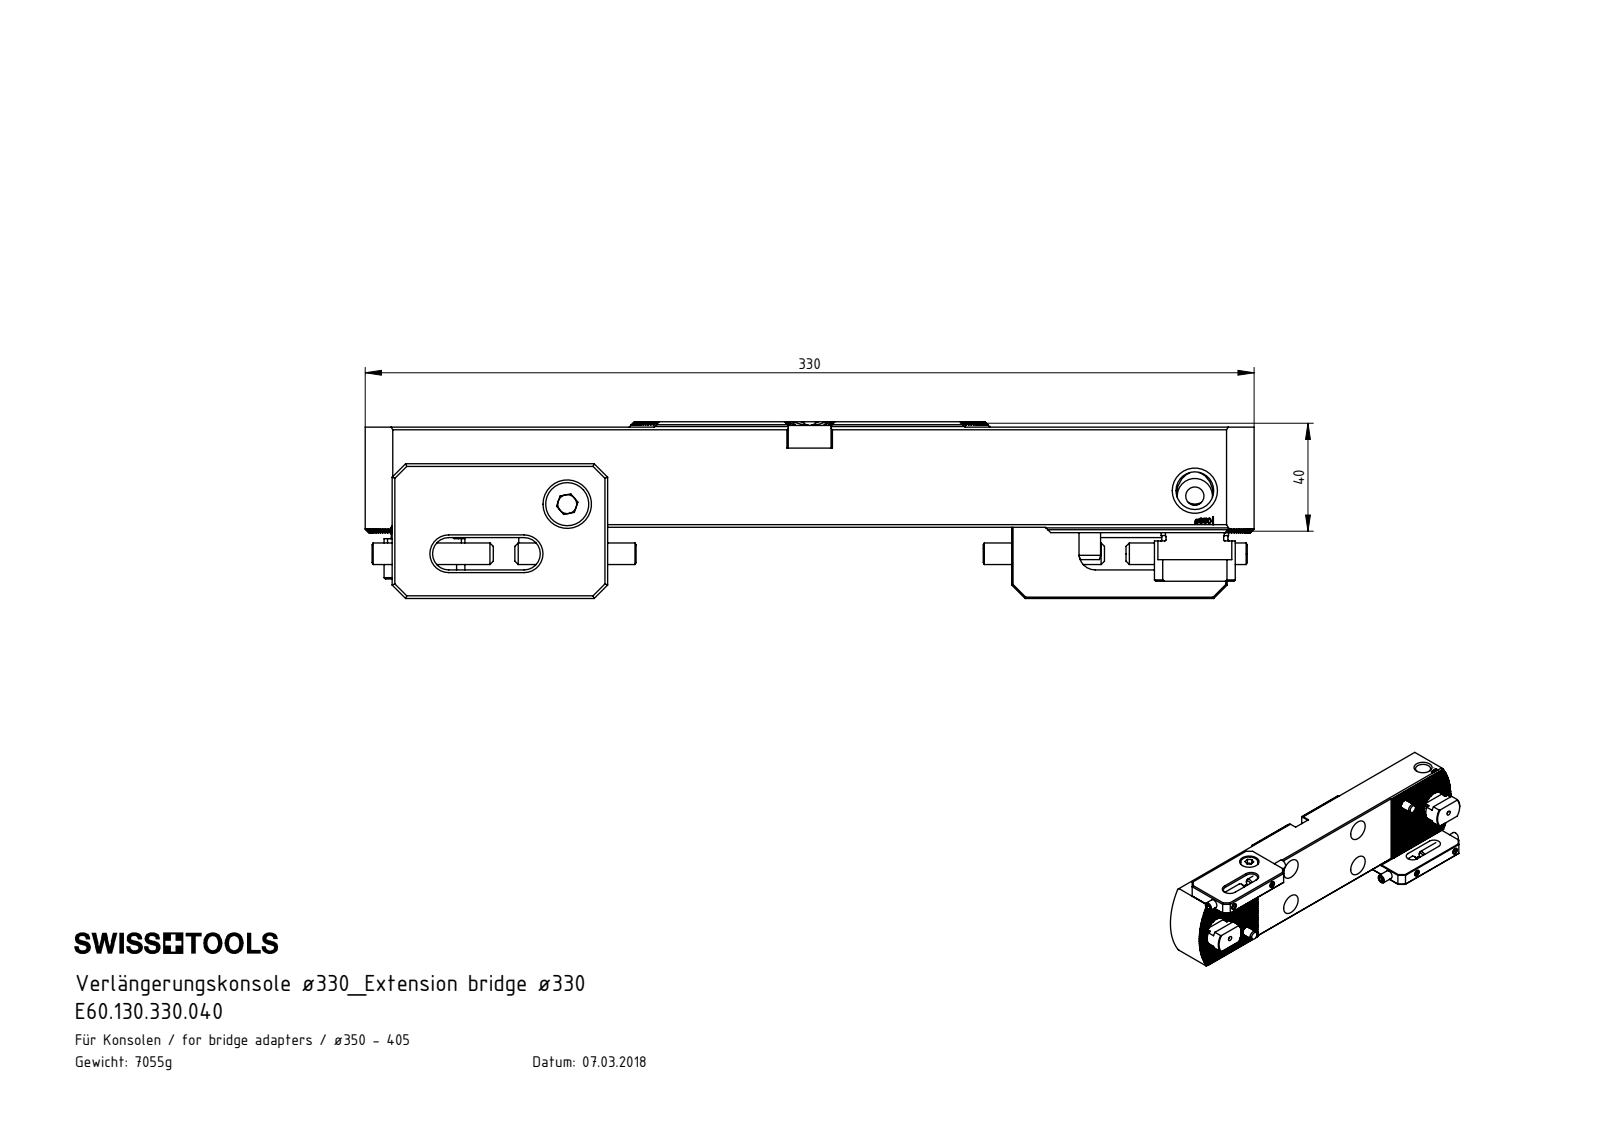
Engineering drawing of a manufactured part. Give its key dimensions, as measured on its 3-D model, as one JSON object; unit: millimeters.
{"part_name": "VK1-ER7.001.012_mit langer Schraube; VK1-ER2.101.010_A; ISO 4766 - M6x12_ISO 4766 - M6 x 10; VK1-ER2.001.044_A (+8 more)", "step_written_by": "SolidWorks 2017 (CONFIG_CONTROL_DESIGN)", "units": "millimeters", "bodies": {"solids": 26, "faces": 1569, "planar": 866, "cylindrical": 400, "other": 303}, "overall_size": [330, 94, 65.58], "volume_mm3": 904748, "surface_area_mm2": 153746, "round_holes": [[5, 4], [6, 4], [6.8, 4], [13, 4], [19, 4], [2, 2], [8, 2], [8.5, 2], [10.5, 2], [11, 2], [14, 2], [18, 2]], "round_bosses_or_shafts": [[6, 4], [16, 3], [10, 2], [8, 2]], "partial_cylinders_radius": [[0.14, 66], [2, 8], [6, 4], [12.3, 2], [15, 2], [65, 2], [7.95, 1]], "face_to_face_distances": [70, 37.16, 12, 82, 1.73, 8.66, 3.46, 6.93, 41.57, 11.5], "hole_center_spacings": [101, 188.07, 286, 7.9, 18.55, 19.61, 34.53, 35.09]}
